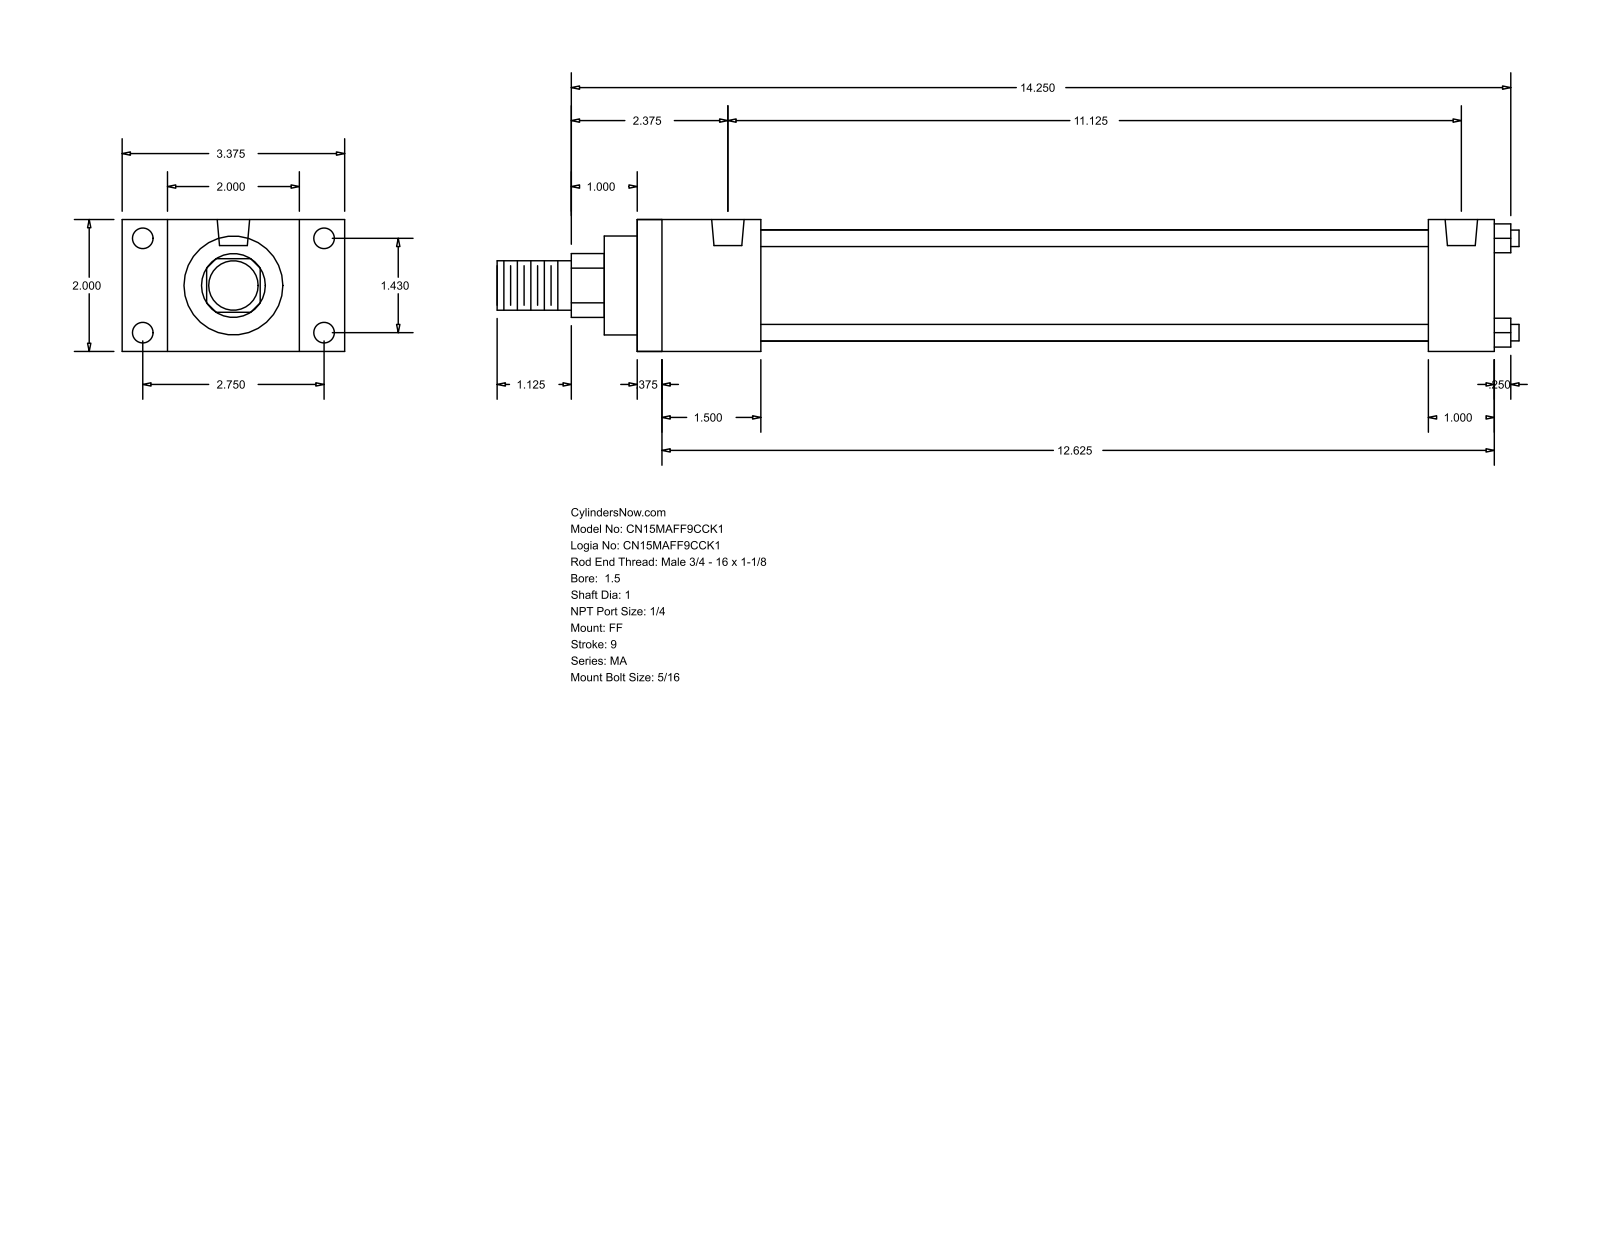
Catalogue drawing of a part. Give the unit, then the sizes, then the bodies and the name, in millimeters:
Units: millimetres
Overall size (bounding box): 393.7 × 85.72 × 50.8
Round holes (diameter × count): ⌀7.94 ×8, ⌀12.49 ×2
Round bosses / shafts (diameter × count): ⌀6.35 ×4, ⌀42.93 ×1, ⌀38.1 ×1, ⌀25.4 ×1, ⌀19.05 ×1
Partial cylindrical surfaces — rounded edges, fillets, slot ends (radius × count): R12.29 ×1
Main face-to-face distances: 50.8, 330.2, 9.52, 320.68, 25.4, 47.63, 304.8, 38.11, 295.28, 257.17
Hole centre spacings: 36.32, 69.84, 78.72, 282.57
Bodies: 0 solids, 92 faces (64 planar, 28 cylindrical, 0 other)
Part name (STEP PRODUCT): MA_FF__0150_1
STEP written by: GSSL Pune (CONFIG_CONTROL_DESIGN)
